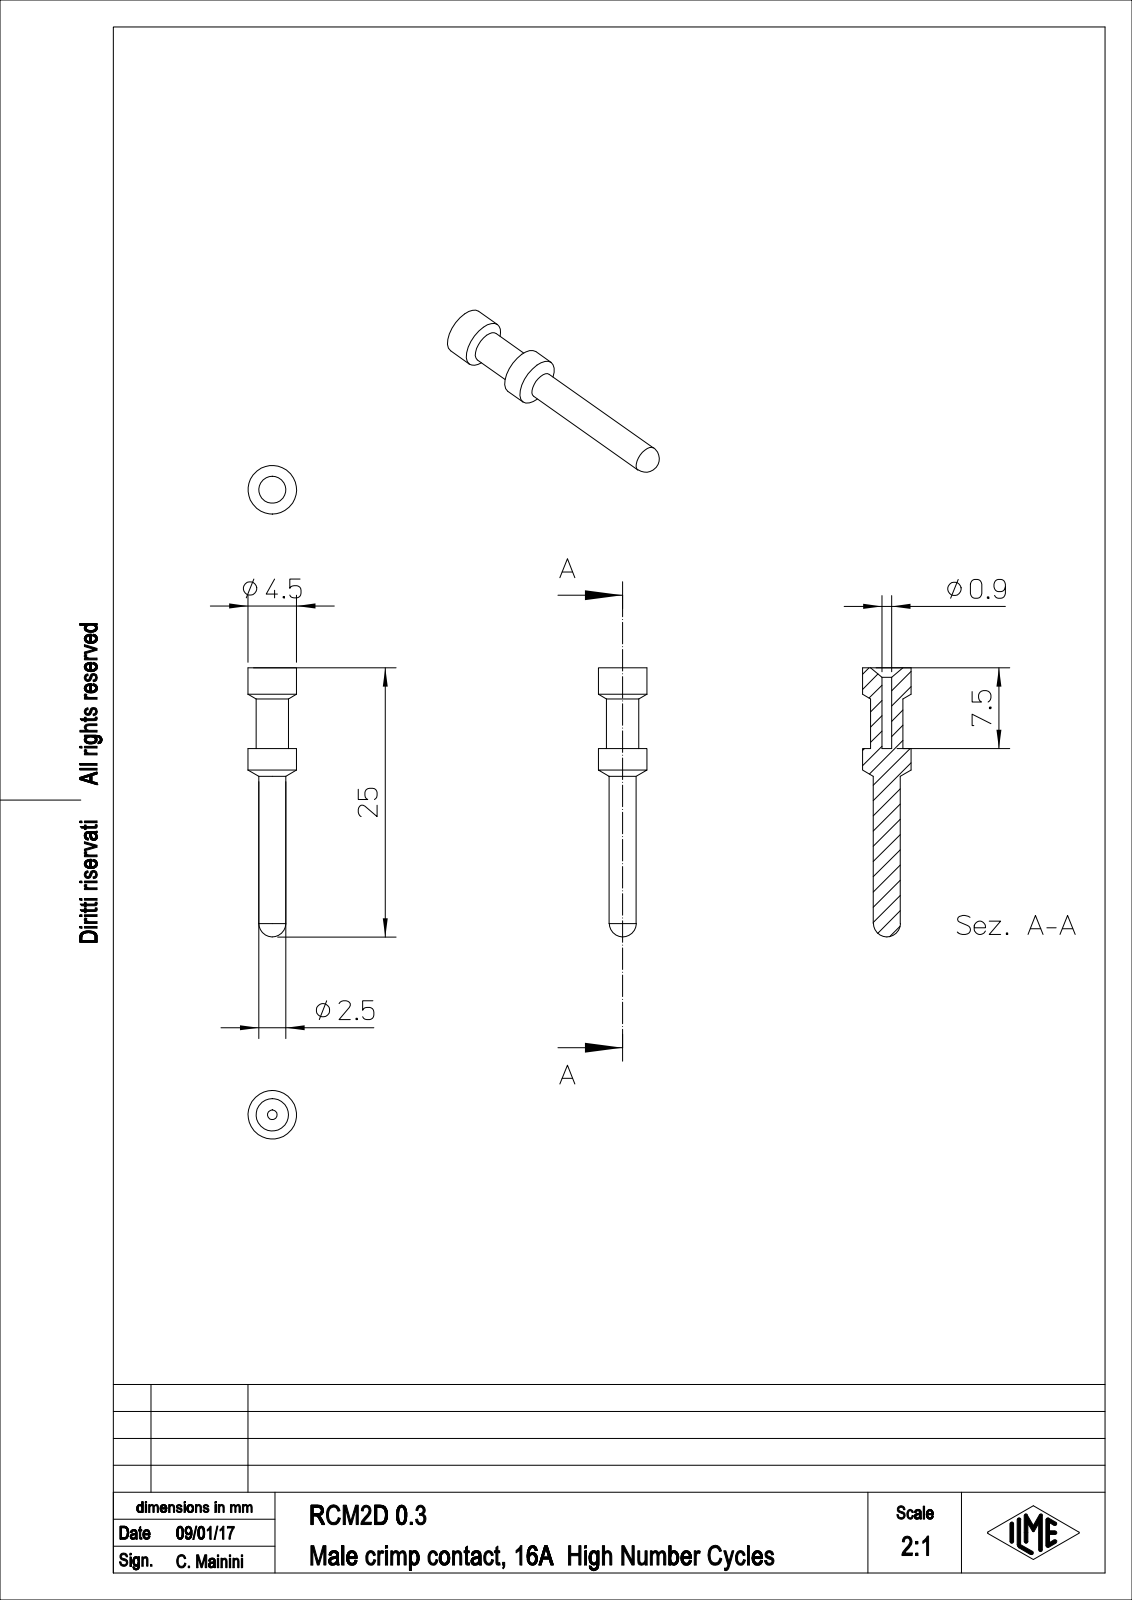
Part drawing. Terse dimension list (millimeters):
name: RCM2D_0.3
written by: PTC Creo Elements/Direct Modeling 19.0E 27-Jun-2016 (C) Parametric Technology GmbH (AUTOMOTIVE_DESIGN)
unit: mm
bodies: 1 solid, 21 faces (3 planar, 10 cylindrical, 8 other)
size: 25 × 4.5 × 4.5
volume: 178 mm³; area: 292 mm²
holes: 1× ⌀0.9
bosses: 1× ⌀4.5, 1× ⌀3, 1× ⌀2.5
face distances: 7.5
